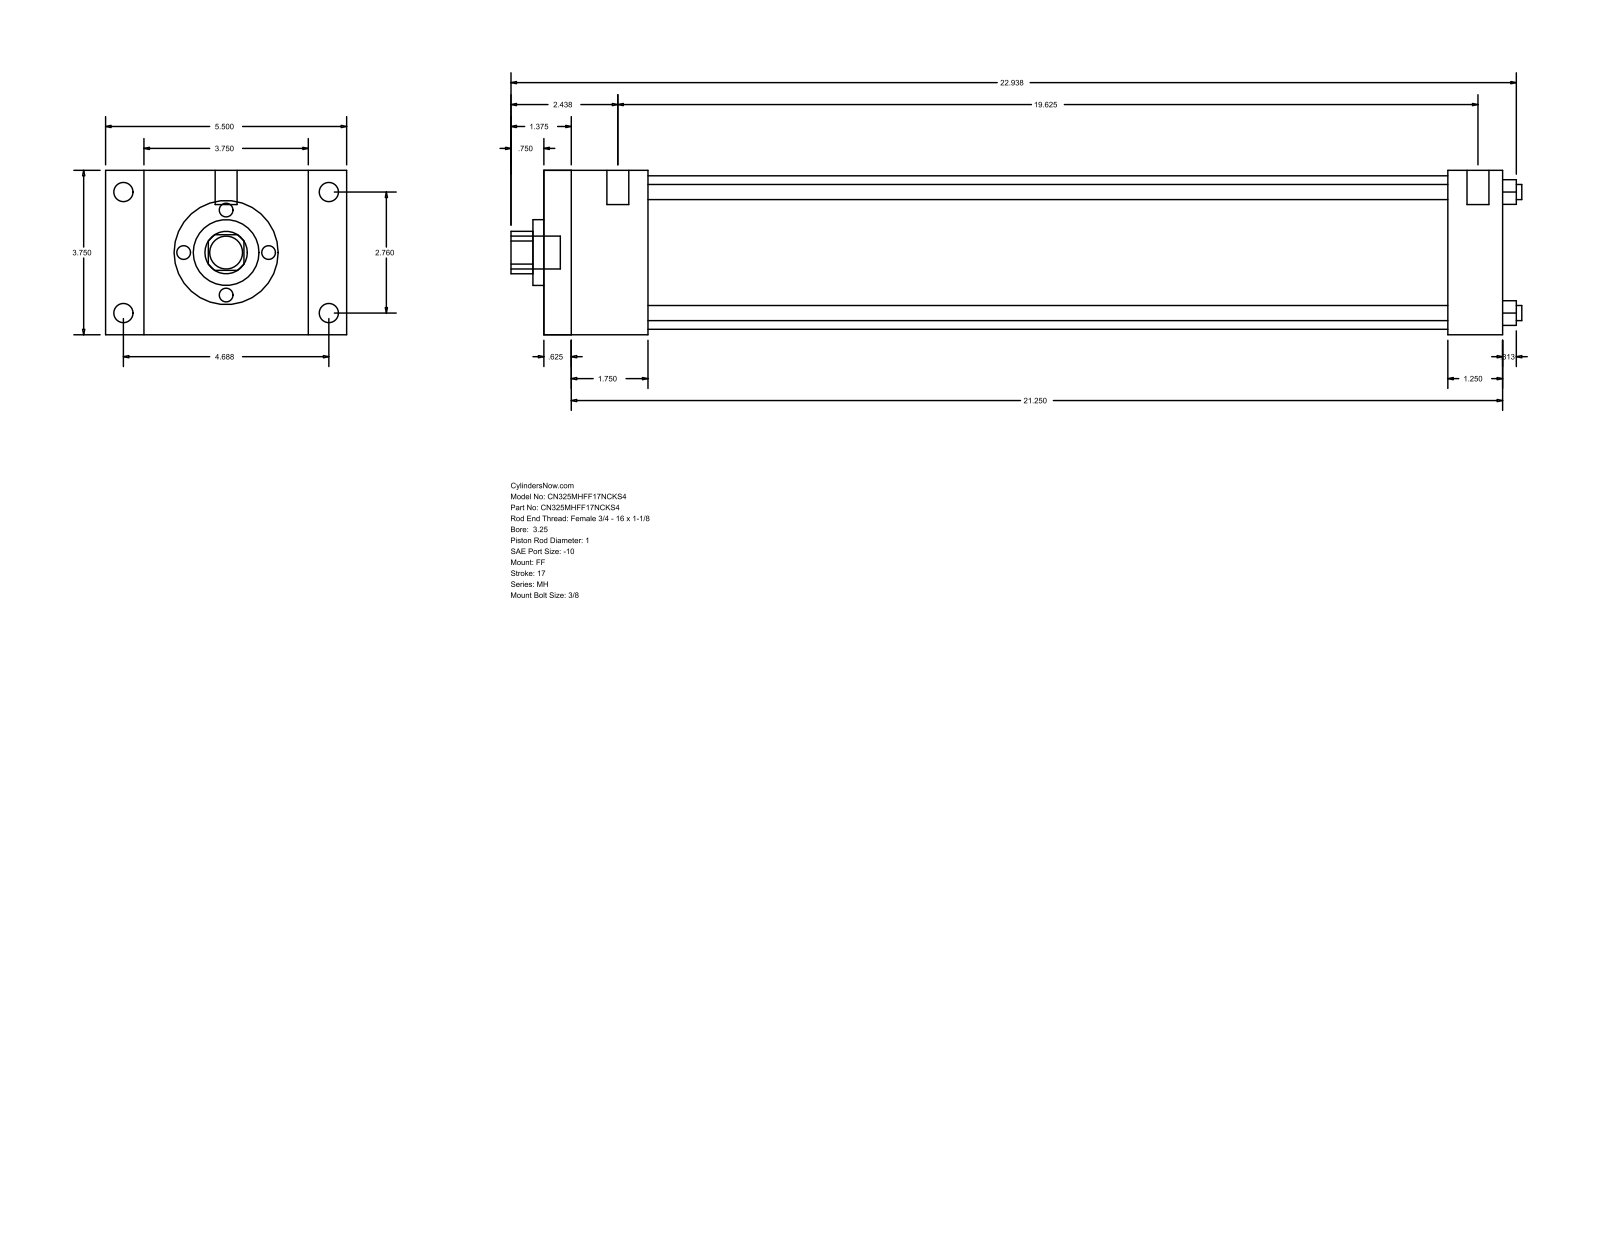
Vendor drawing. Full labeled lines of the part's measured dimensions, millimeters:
Part name (STEP PRODUCT): MH_FF__0325_1
STEP written by: GSSL Pune (CONFIG_CONTROL_DESIGN)
Units: millimetres
Bodies: 0 solids, 92 faces (64 planar, 28 cylindrical, 0 other)
Overall size (bounding box): 585.79 × 139.7 × 95.25
Round holes (diameter × count): ⌀8.76 ×4, ⌀25.4 ×1, ⌀38.1 ×1, ⌀88.9 ×1
Round bosses / shafts (diameter × count): ⌀11.13 ×4, ⌀5.56 ×4, ⌀12.7 ×2, ⌀19.05 ×1
Partial cylindrical surfaces — rounded edges, fillets, slot ends (radius × count): R12.29 ×1
Main face-to-face distances: 95.24, 555.62, 15.87, 539.75, 22.23, 117.47, 523.87, 508, 31.75, 60.33
Hole centre spacings: 49.57, 70.1, 99.14
